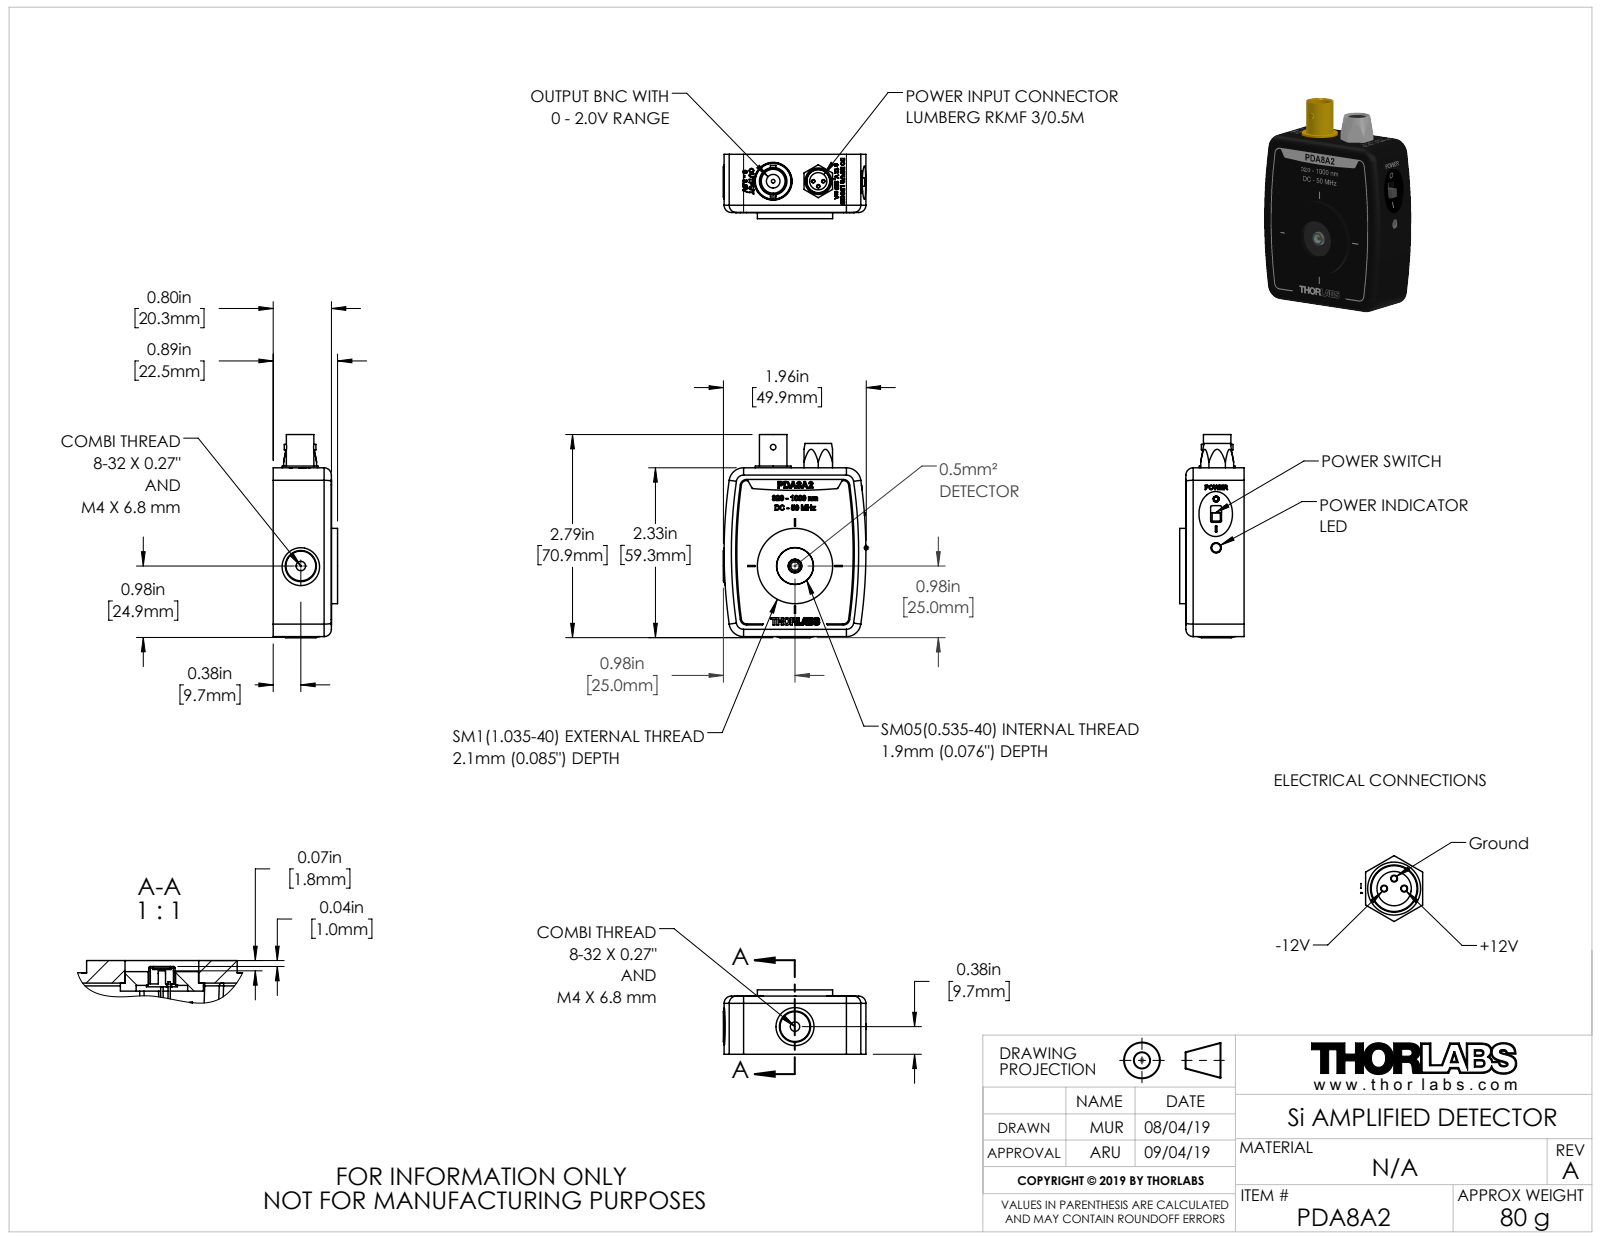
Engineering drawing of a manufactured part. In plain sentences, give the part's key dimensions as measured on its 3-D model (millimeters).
The part is named "19.04.16_PDA8A2_A". Its 3-D file was written by "SolidWorks 2018 (AUTOMOTIVE_DESIGN)". It is 0 solids with 4135 faces: 2083 planar, 311 cylindrical and 1741 other. Overall it measures 70.9 by 49.89 by 22.48 millimeters. Round holes: 7 of diameter 1.78, 3 of diameter 1, 3 of diameter 1.02, 2 of diameter 3.3, 1 of diameter 0.38, 1 of diameter 0.89, 1 of diameter 1.27, 1 of diameter 2.4, 1 of diameter 2.92, 1 of diameter 3, 1 of diameter 3.56, 1 of diameter 4.04. Round bosses or shafts: 4 of diameter 5, 4 of diameter 2.18, 3 of diameter 0.43, 1 of diameter 26.29, 1 of diameter 14.5, 1 of diameter 12.8, 1 of diameter 12.5, 1 of diameter 9.6. Partial cylindrical surfaces (rounded edges, fillets, slot ends): 18 of radius 0.51, 8 of radius 0.76, 8 of radius 2.54, 4 of radius 0.56, 4 of radius 1.6, 4 of radius 1.85, 4 of radius 2.23, 4 of radius 4.06. The main face-to-face distances are 1.5, 18.44, 16.94, 1.78, 18.72, 20.22, 58.93, 3.94, 2.16, 20.88. The hole center spacings are 1.27, 1.75, 1.8, 2.47, 19.36, 19.81, 20.99, 27.19.
